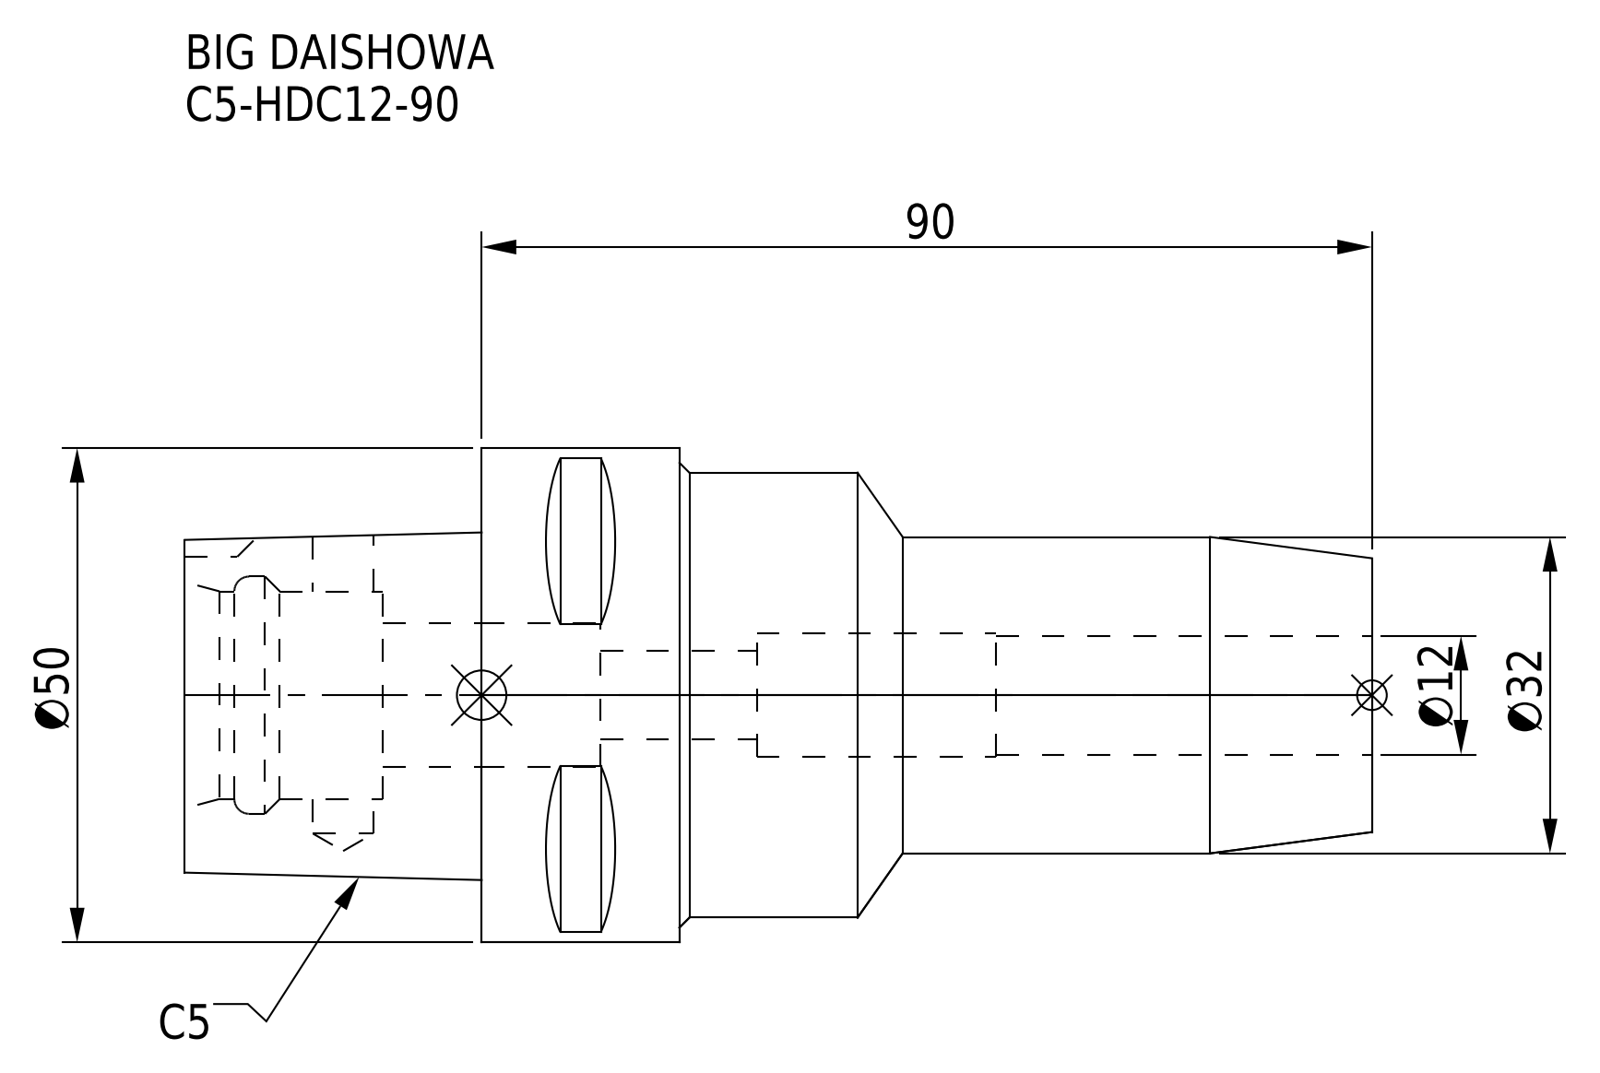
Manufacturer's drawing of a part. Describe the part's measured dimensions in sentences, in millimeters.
The part is named "C5-HDC12-90". Its 3-D file was written by "CREO PARAMETRIC BY PTC INC, 2016380 (AUTOMOTIVE_DESIGN)". It is 1 solid with 71 faces: 30 planar, 25 cylindrical and 16 other. Overall it measures 120 by 50 by 50 millimeters. Its volume is 116 736 cubic millimeters and its surface area 22 804 square millimeters. Round holes: 1 of diameter 6.1, 1 of diameter 9, 1 of diameter 12, 1 of diameter 12.5, 1 of diameter 14.5, 1 of diameter 21, 1 of diameter 24. Round bosses or shafts: 1 of diameter 50, 1 of diameter 45, 1 of diameter 32. Partial cylindrical surfaces (rounded edges, fillets, slot ends): 1 of radius 4. The main face-to-face distances are 30, 90, 20, 120, 70, 50, 44, 100, 10, 19.18.
